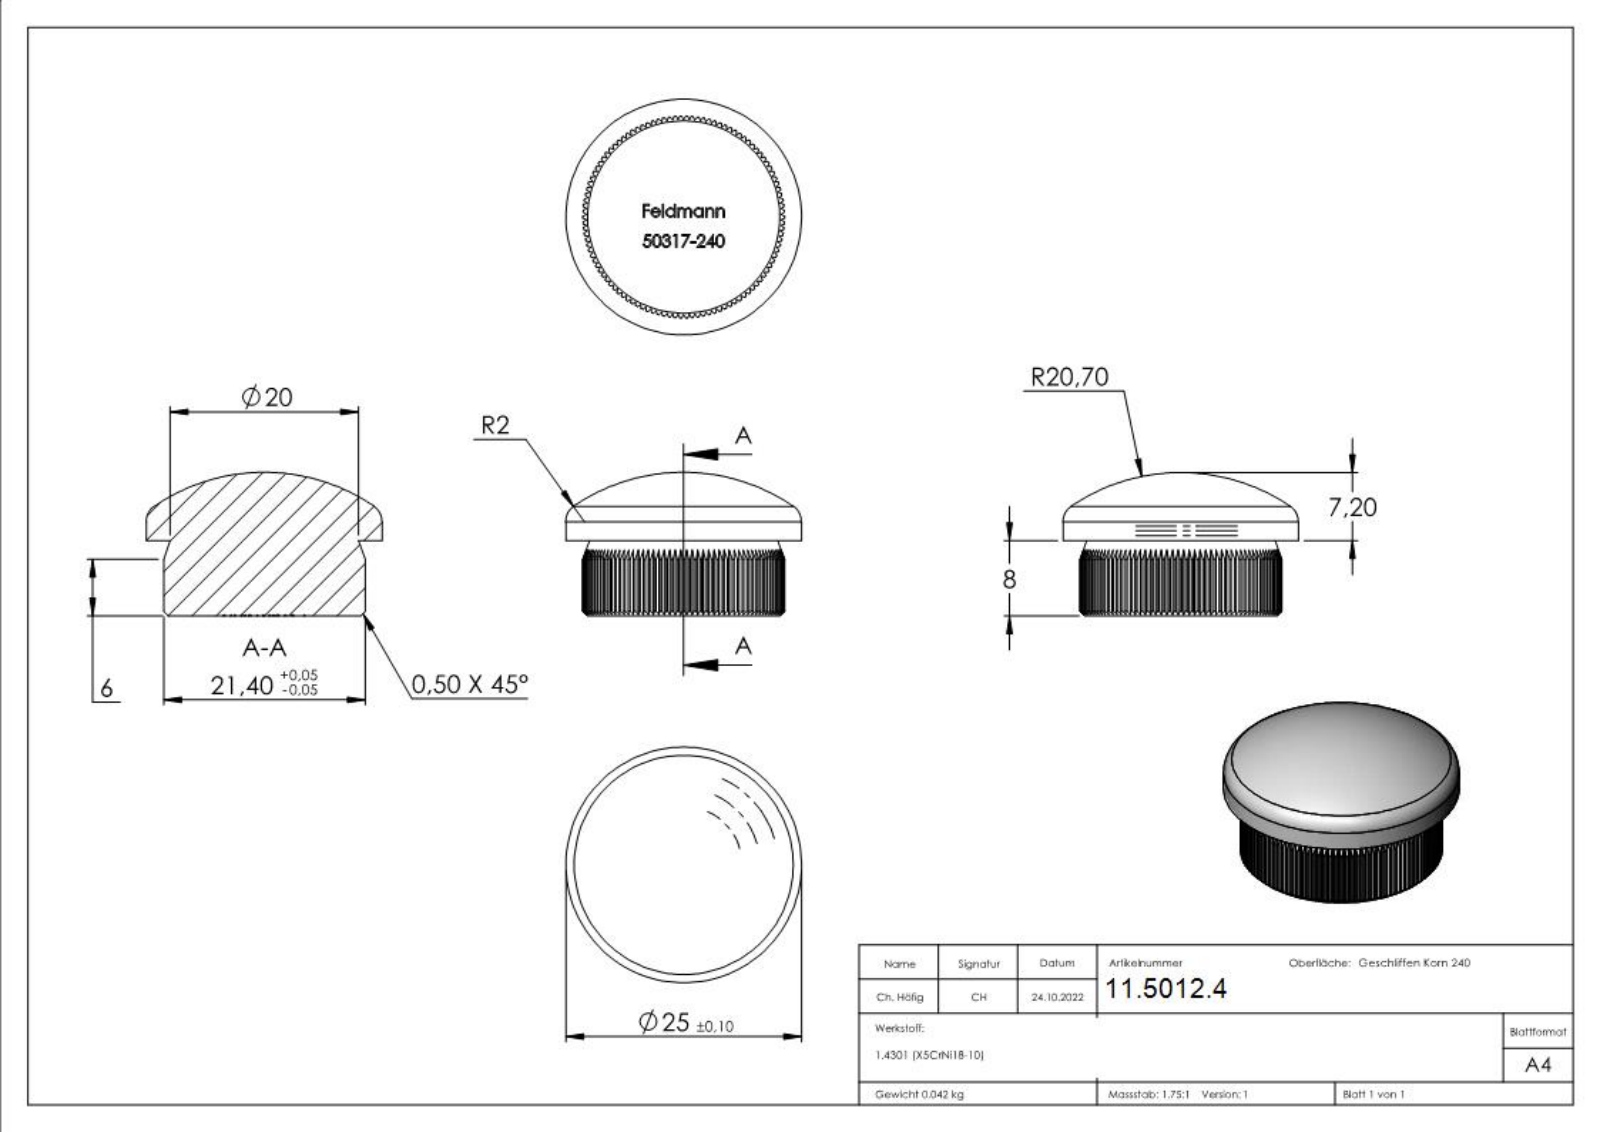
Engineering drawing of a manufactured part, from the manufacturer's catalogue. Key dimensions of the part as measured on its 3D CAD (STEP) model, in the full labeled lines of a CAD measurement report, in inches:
Part name (STEP PRODUCT): 50317-240
STEP written by: SolidWorks 2018 (CONFIG_CONTROL_DESIGN)
Units: inches
Bodies: 1 solid, 552 faces (343 planar, 111 cylindrical, 98 other)
Overall size (bounding box): 0.984 × 0.984 × 0.598
Volume: 0.324 in³ · Surface area: 3.261 in²
Round bosses / shafts (diameter × count): ⌀0.984 ×1
Partial cylindrical surfaces — rounded edges, fillets, slot ends (radius × count): R0.421 ×1
Main face-to-face distances: 0.315, 0.408, 0.407, 0.311, 0.117, 0.015, 0.055, 0.133, 0.047, 0.126
